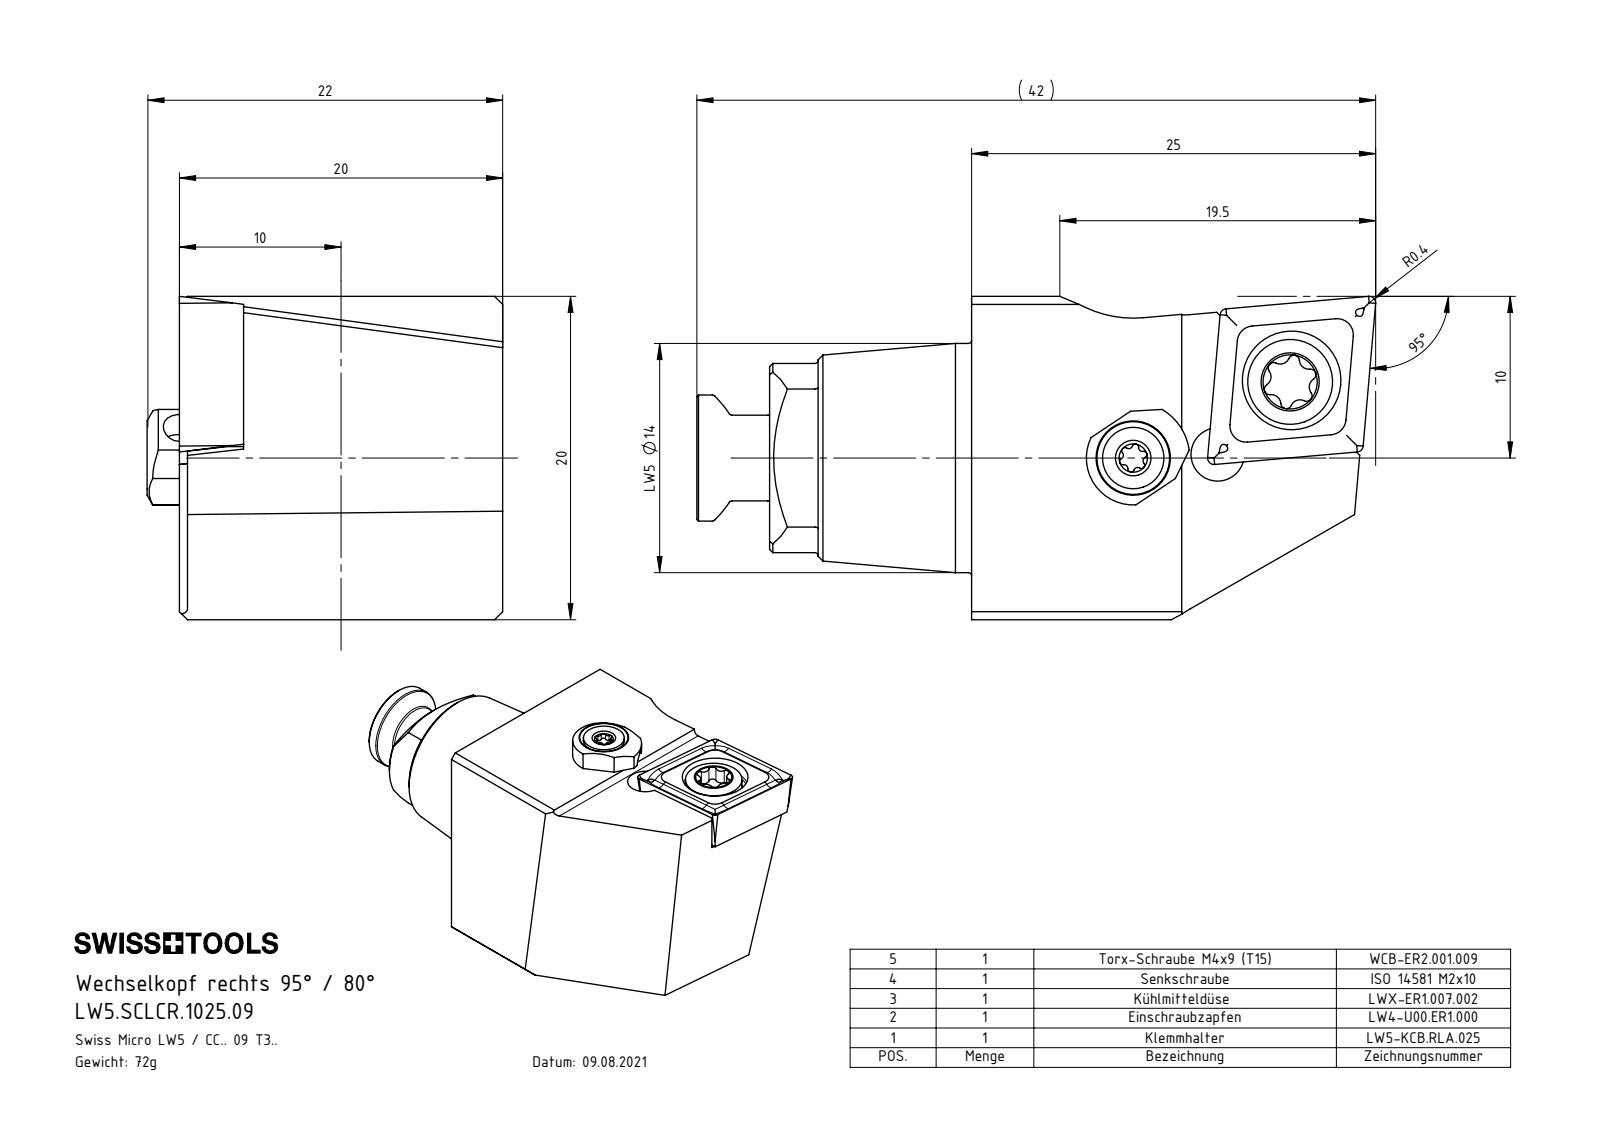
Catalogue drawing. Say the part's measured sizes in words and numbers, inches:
The part is named "LW5-KCB.RLA.025_A; LW5.SCLCR.1025.09; LW4-U00.ER1.000_B; WCB-ER2.001.009_A (+3 more)". Its 3-D file was written by "SolidWorks 2022 (CONFIG_CONTROL_DESIGN)". It is 6 solids with 263 faces: 69 planar, 81 cylindrical and 113 other. Overall it measures 1.654 by 0.866 by 0.787 inches. Its volume is 0.558 cubic inches and its surface area 6.853 square inches. Round holes: 2 of diameter 0.118, 2 of diameter 0.13, 1 of diameter 0.063, 1 of diameter 0.079, 1 of diameter 0.098, 1 of diameter 0.173, 1 of diameter 0.217, 1 of diameter 0.24. Round bosses or shafts: 1 of diameter 0.558, 1 of diameter 0.303, 1 of diameter 0.236, 1 of diameter 0.209, 1 of diameter 0.207, 1 of diameter 0.197, 1 of diameter 0.157, 1 of diameter 0.15. Partial cylindrical surfaces (rounded edges, fillets, slot ends): 8 of radius 0.008, 6 of radius 0.009, 6 of radius 0.013, 6 of radius 0.023, 1 of radius 0.02, 1 of radius 0.039, 1 of radius 0.114, 1 of radius 0.138. The main face-to-face distances are 0.787, 0.631, 0.156, 0.768, 0.137, 0.02, 0.295, 0.079, 0.118, 0.492. The hole center spacings are 0.206, 0.25, 0.255, 0.425, 0.43.
